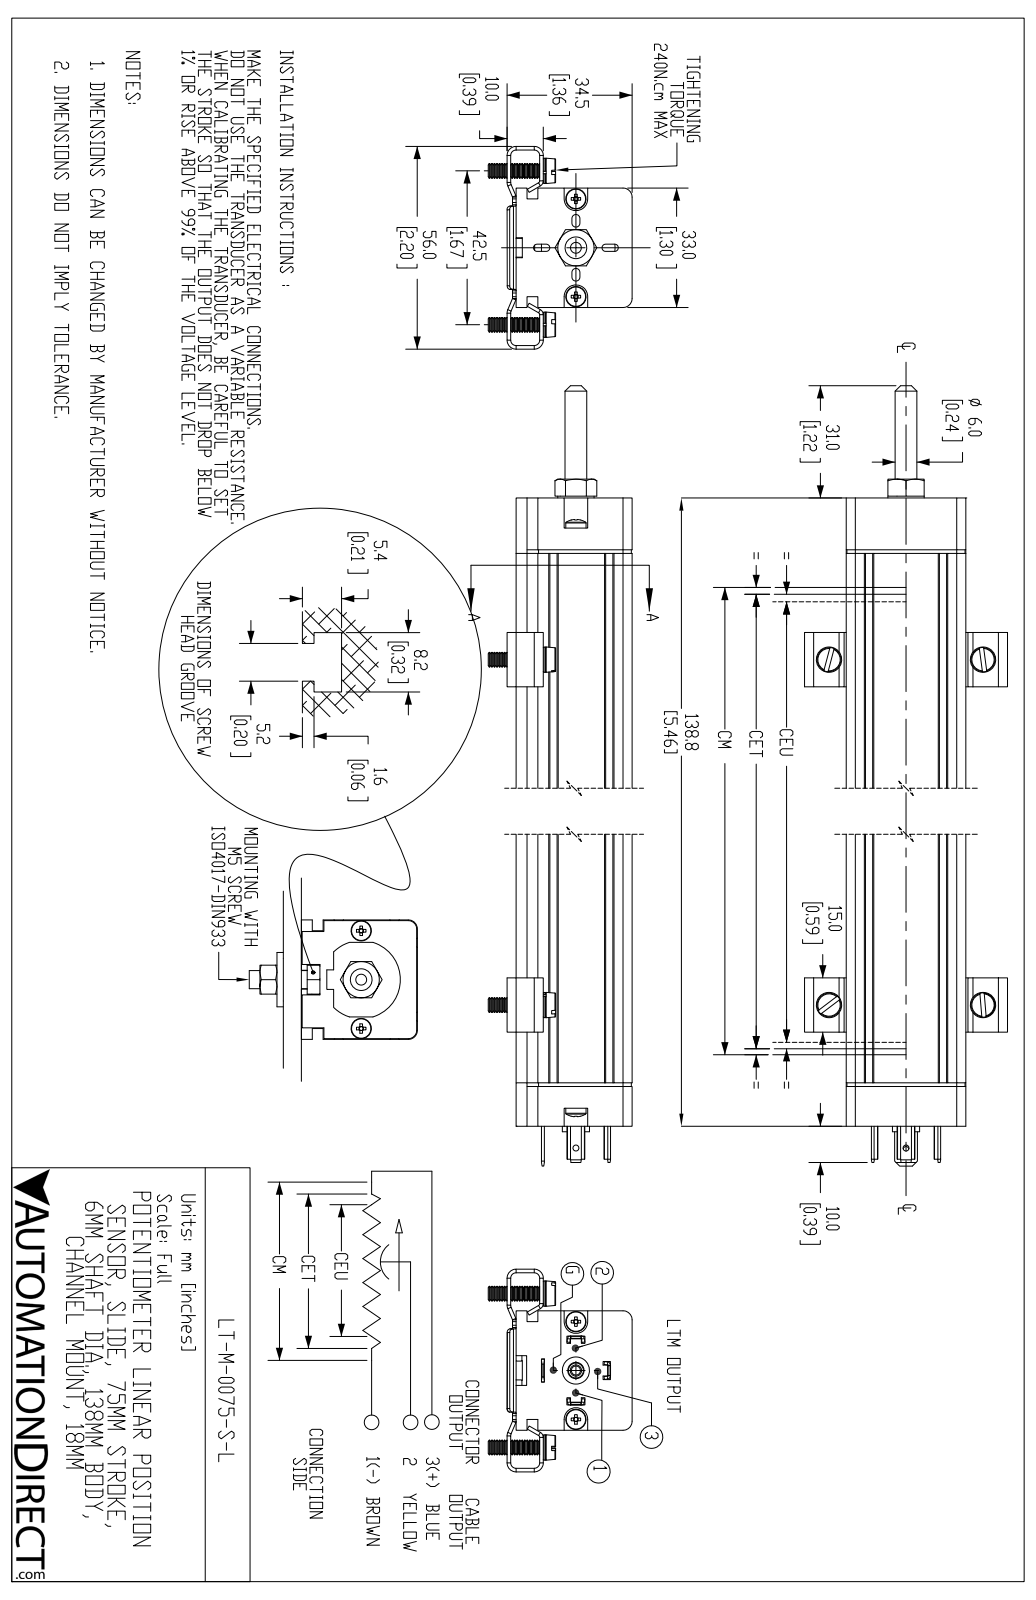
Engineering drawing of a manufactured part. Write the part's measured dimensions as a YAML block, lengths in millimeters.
part_name: "LT-M-0075-S-L"
step_written_by: "SolidWorks 2019 (AUTOMOTIVE_DESIGN)"
units: millimeters
bodies: {solids: 21, faces: 1620, planar: 696, cylindrical: 356, other: 568}
overall_size: [198.4, 56, 39.7]
volume: 143000
surface_area: 42510
round_holes:
  - {diameter: 3.6, count: 4}
  - {diameter: 1.5, count: 2}
  - {diameter: 1.7, count: 2}
  - {diameter: 2.7, count: 2}
  - {diameter: 3.4, count: 2}
  - {diameter: 4.3, count: 2}
  - {diameter: 1.6, count: 1}
  - {diameter: 2.5, count: 1}
  - {diameter: 3, count: 1}
  - {diameter: 4.1, count: 1}
  - {diameter: 5, count: 1}
  - {diameter: 7, count: 1}
round_bosses_or_shafts:
  - {diameter: 7, count: 4}
  - {diameter: 4, count: 4}
  - {diameter: 5.6, count: 2}
  - {diameter: 3, count: 2}
  - {diameter: 7.5, count: 1}
  - {diameter: 6, count: 1}
  - {diameter: 4.5, count: 1}
  - {diameter: 4.4, count: 1}
partial_cylinders:
  - {radius: 1, count: 34}
  - {radius: 2.5, count: 12}
  - {radius: 1.5, count: 10}
  - {radius: 2.2, count: 8}
  - {radius: 0.8, count: 6}
  - {radius: 1.1, count: 4}
  - {radius: 0.6, count: 2}
  - {radius: 1.6, count: 2}
face_to_face_distances: [33, 32, 1, 3, 1.5, 32.7, 0.5, 5.4, 7.5, 26]
hole_center_spacings: [12.3, 13.5, 34.5, 42.2, 42.5, 44.9, 45.2, 71.8]
